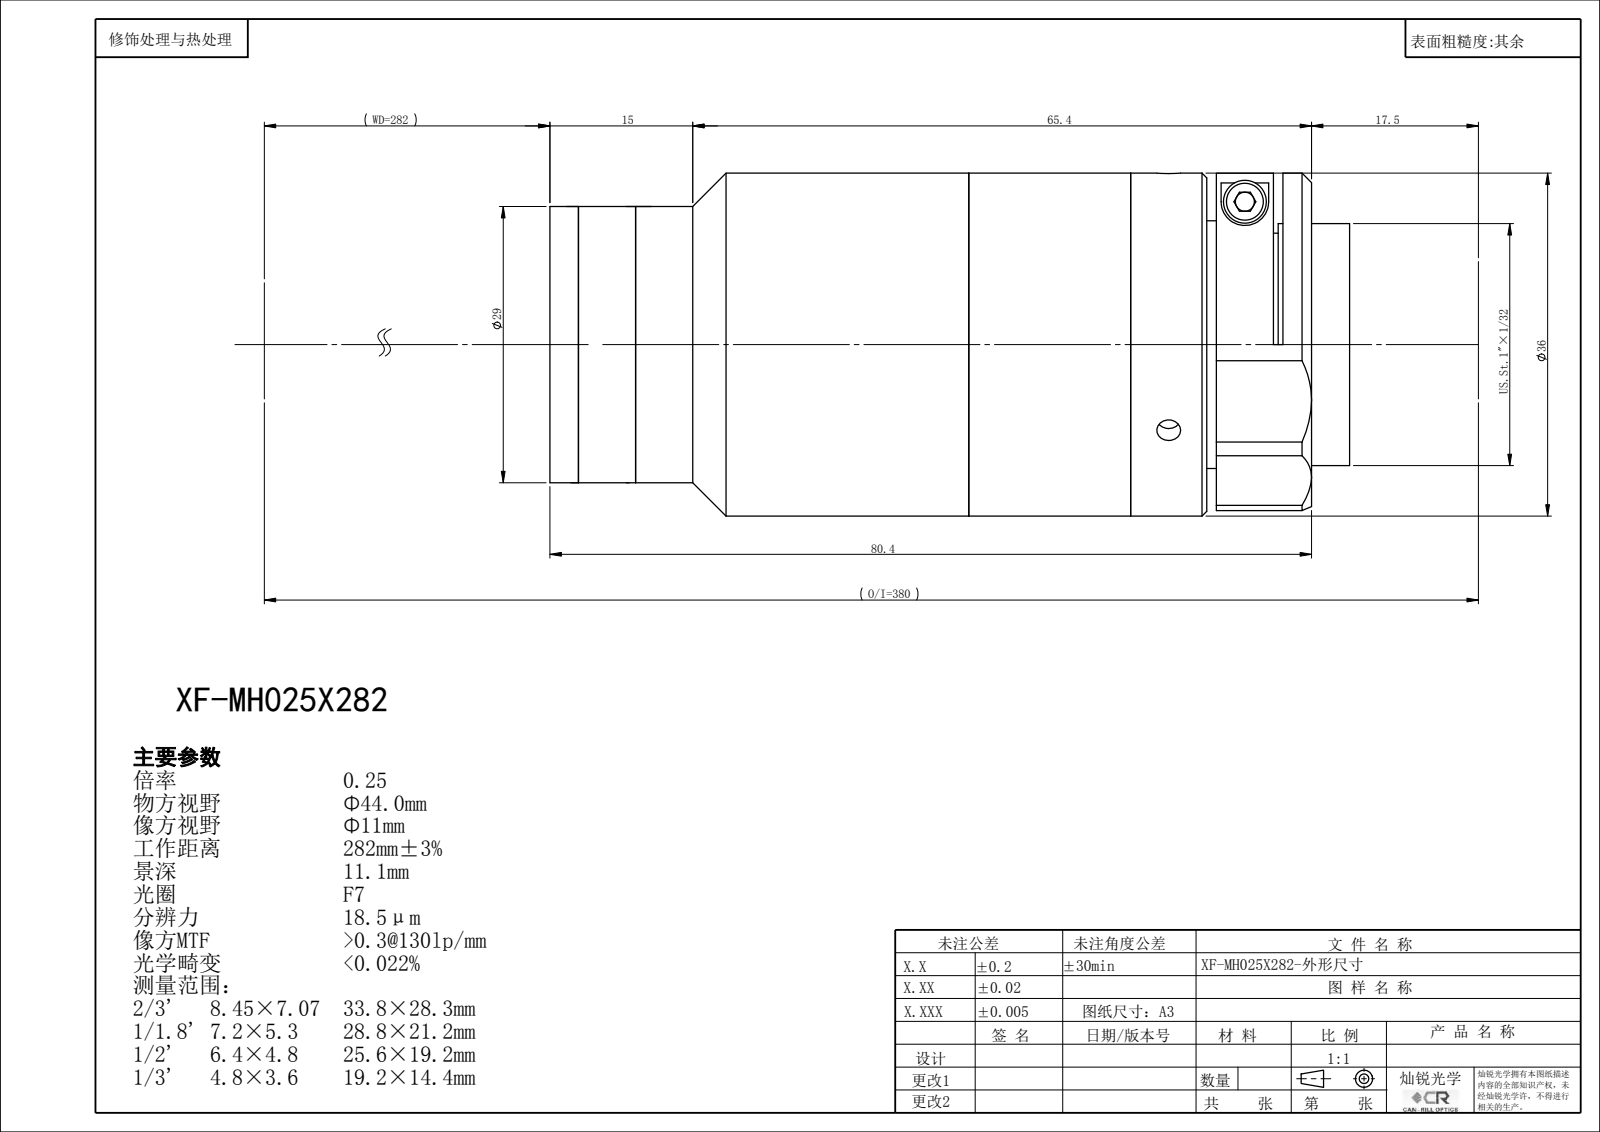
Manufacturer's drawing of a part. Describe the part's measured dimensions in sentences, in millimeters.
The part is named "XF-MH025X282". Its 3-D file was written by "SolidWorks 2022 (CONFIG_CONTROL_DESIGN)". It is 0 solids with 128 faces: 66 planar, 40 cylindrical and 22 other. Overall it measures 84.41 by 36 by 36 millimeters. Round holes: 3 of diameter 2.5, 1 of diameter 18, 1 of diameter 22.4, 1 of diameter 24, 1 of diameter 24.9, 1 of diameter 26.4. Round bosses or shafts: 1 of diameter 36, 1 of diameter 34, 1 of diameter 29, 1 of diameter 25.4. The main face-to-face distances are 19.41, 1.5, 17.91, 17, 34.91, 36.41, 75.41, 40.5, 57.5, 76.91.
